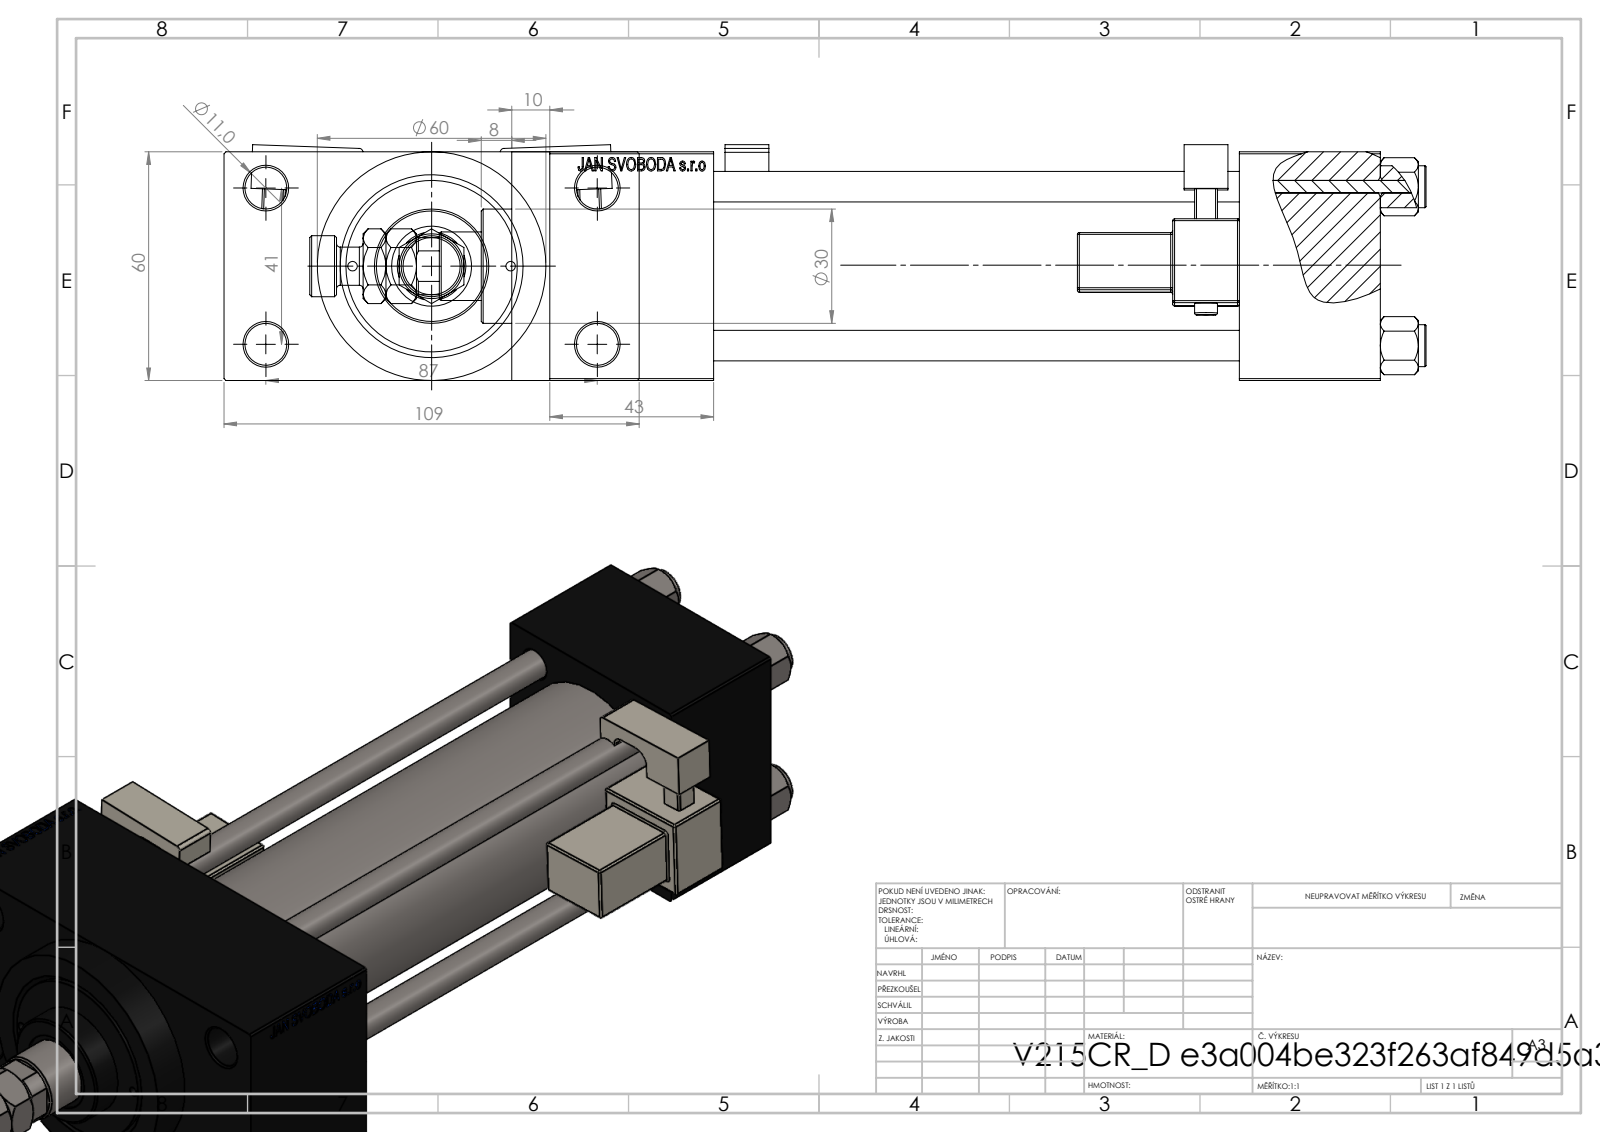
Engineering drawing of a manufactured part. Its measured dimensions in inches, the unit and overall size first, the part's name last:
Units: inches
Overall size (bounding box): 11.535 × 4.291 × 2.437
Round holes (diameter × count): ⌀0.315 ×4, ⌀0.433 ×4, ⌀0.098 ×2, ⌀0.276 ×2, ⌀0.656 ×2, ⌀0.945 ×2, ⌀0.335 ×1, ⌀0.709 ×1, ⌀0.827 ×1, ⌀1.22 ×1, ⌀1.575 ×1, ⌀1.772 ×1
Round bosses / shafts (diameter × count): ⌀0.433 ×4, ⌀0.236 ×2, ⌀2.362 ×1, ⌀1.811 ×1, ⌀1.181 ×1, ⌀0.63 ×1, ⌀0.394 ×1
Partial cylindrical surfaces — rounded edges, fillets, slot ends (radius × count): R0.02 ×48, R0.039 ×2, R0.098 ×2, R0.157 ×2, R0.335 ×1
Main face-to-face distances: 2.362, 5.433, 0.965, 3.327, 1.457, 6.89, 8.583, 7.126, 1.693, 4.291
Hole centre spacings: 0.821, 0.892, 1.161, 1.206, 1.642, 1.832, 1.856, 1.893
Volume: 38.29 in³ · Surface area: 264.8 in²
Bodies: 14 solids, 1318 faces (574 planar, 156 cylindrical, 588 other)
Part name (STEP PRODUCT): NUT_M5_D; V215CR_D_Body; V215CR_MSU; V215CR_VCP_D (+3 more)
STEP written by: SolidWorks 2019 (CONFIG_CONTROL_DESIGN)
